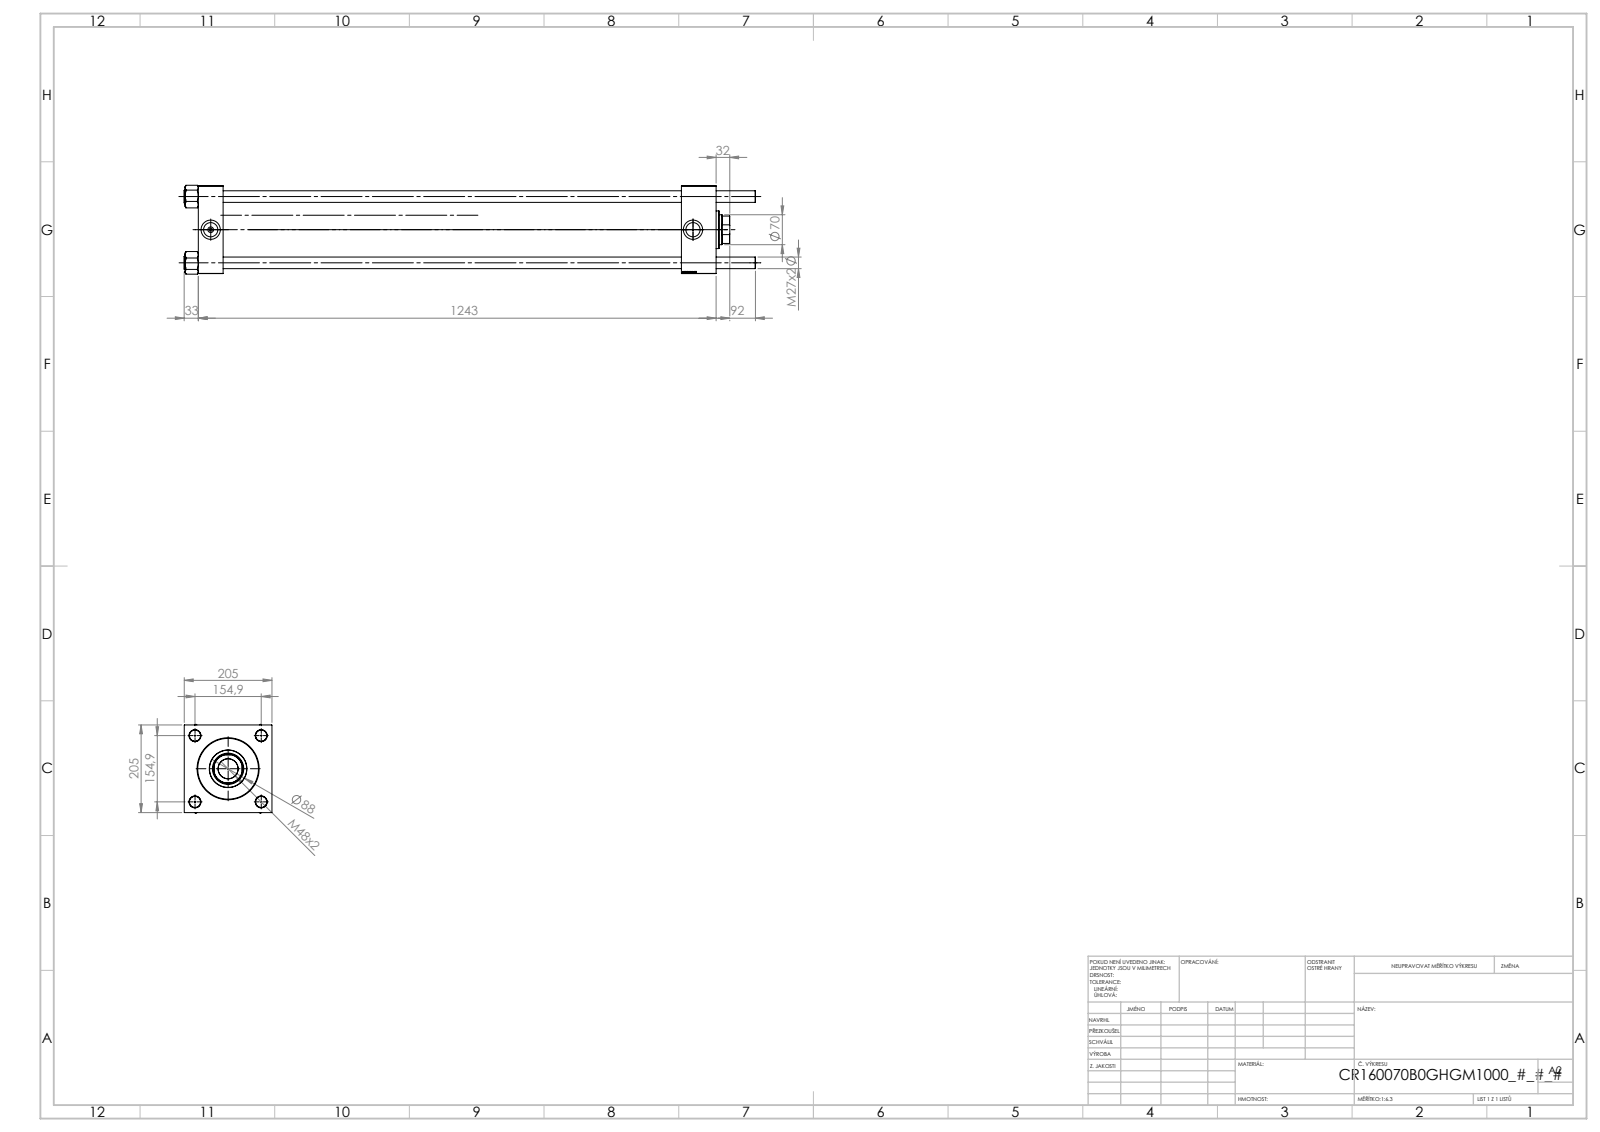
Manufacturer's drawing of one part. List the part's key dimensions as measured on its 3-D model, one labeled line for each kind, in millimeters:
Part name (STEP PRODUCT): V215CR_VCP_B; V215CR_B_TYCINKA; NUT_M5_B; V215_VC_A (+1 more)
STEP written by: SolidWorks 2019 (CONFIG_CONTROL_DESIGN)
Units: millimetres
Bodies: 11 solids, 1206 faces (480 planar, 78 cylindrical, 648 other)
Overall size (bounding box): 1336 × 207.94 × 205
Volume: 15 270 000 mm³ · Surface area: 2 306 000 mm²
Round holes (diameter × count): ⌀27 ×4, ⌀7 ×2, ⌀33.24 ×2, ⌀45 ×2, ⌀46.5 ×1, ⌀70 ×1, ⌀73 ×1, ⌀120 ×1, ⌀142 ×1, ⌀160 ×1
Round bosses / shafts (diameter × count): ⌀30 ×4, ⌀166 ×1, ⌀88 ×1
Partial cylindrical surfaces — rounded edges, fillets, slot ends (radius × count): R34 ×1
Main face-to-face distances: 205, 58, 1211, 1153, 1130, 1072, 81, 1182.3, 1124.3, 52.3
Hole centre spacings: 109.53, 154.9, 219.06, 1128
